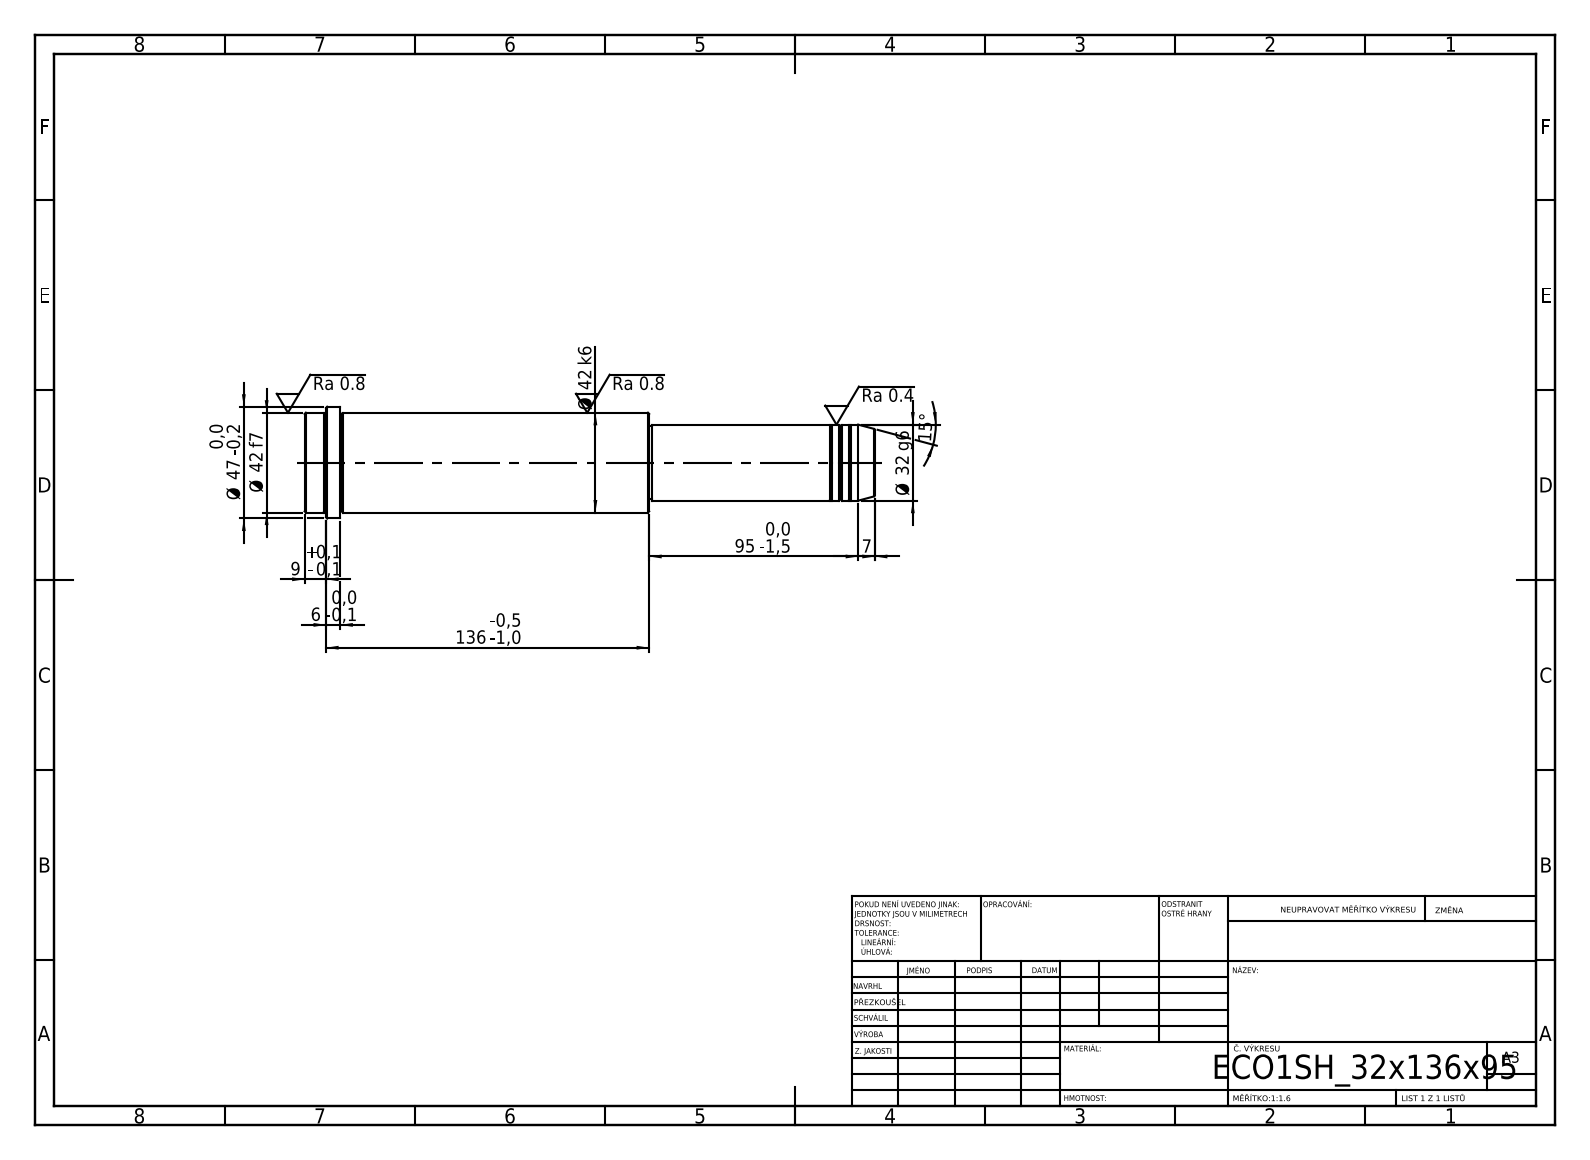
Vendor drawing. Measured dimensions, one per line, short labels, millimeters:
written by: SolidWorks 2019 (CONFIG_CONTROL_DESIGN)
unit: mm
bodies: 1 solid, 52 faces (6 planar, 16 cylindrical, 30 other)
size: 240 × 47 × 47
volume: 278 433 mm³; area: 32 323 mm²
bosses: 1× ⌀47, 1× ⌀42, 1× ⌀32, 1× ⌀31
face distances: 240, 95, 145, 225, 130, 15, 231, 136, 6, 9
